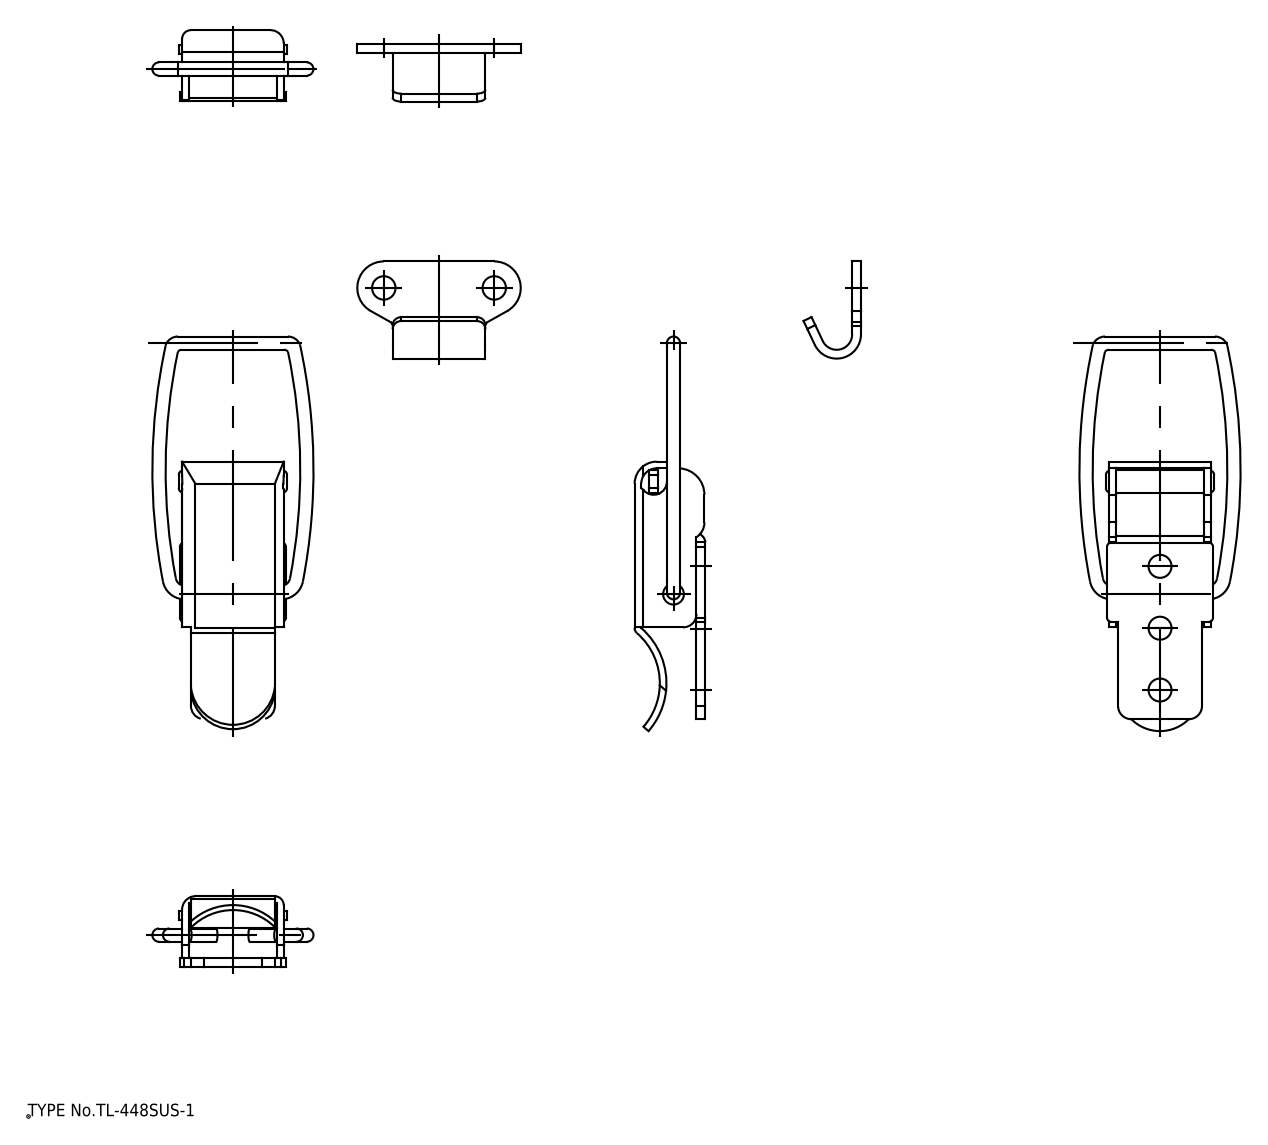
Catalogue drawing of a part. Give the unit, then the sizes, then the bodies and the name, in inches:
Units: inches
Overall size (bounding box): 4.126 × 1.457 × 0.63
Round holes (diameter × count): ⌀0.205 ×3, ⌀0.209 ×2, ⌀0.185 ×1
Round bosses / shafts (diameter × count): ⌀0.118 ×1
Partial cylindrical surfaces — rounded edges, fillets, slot ends (radius × count): R0.039 ×10, R0.079 ×6, R0.059 ×5, R0.118 ×5, R0.236 ×3, R0.138 ×2, R0.157 ×1, R0.197 ×1
Main face-to-face distances: 0.079, 0.059, 0.846, 0.492, 0.571, 0.63, 0.551, 0.787, 0.906, 0.421
Hole centre spacings: 0.551, 2.471, 3.013, 3.558, 0.984, 1.102
Volume: 0.522 in³ · Surface area: 17.44 in²
Bodies: 4 solids, 142 faces (65 planar, 58 cylindrical, 19 other)
Part name (STEP PRODUCT): TL_176SUS_6; アーム; ベース; レバー
STEP written by: spGate 20.6.3 (****-****-****-****) (AUTOMOTIVE_DESIGN)
